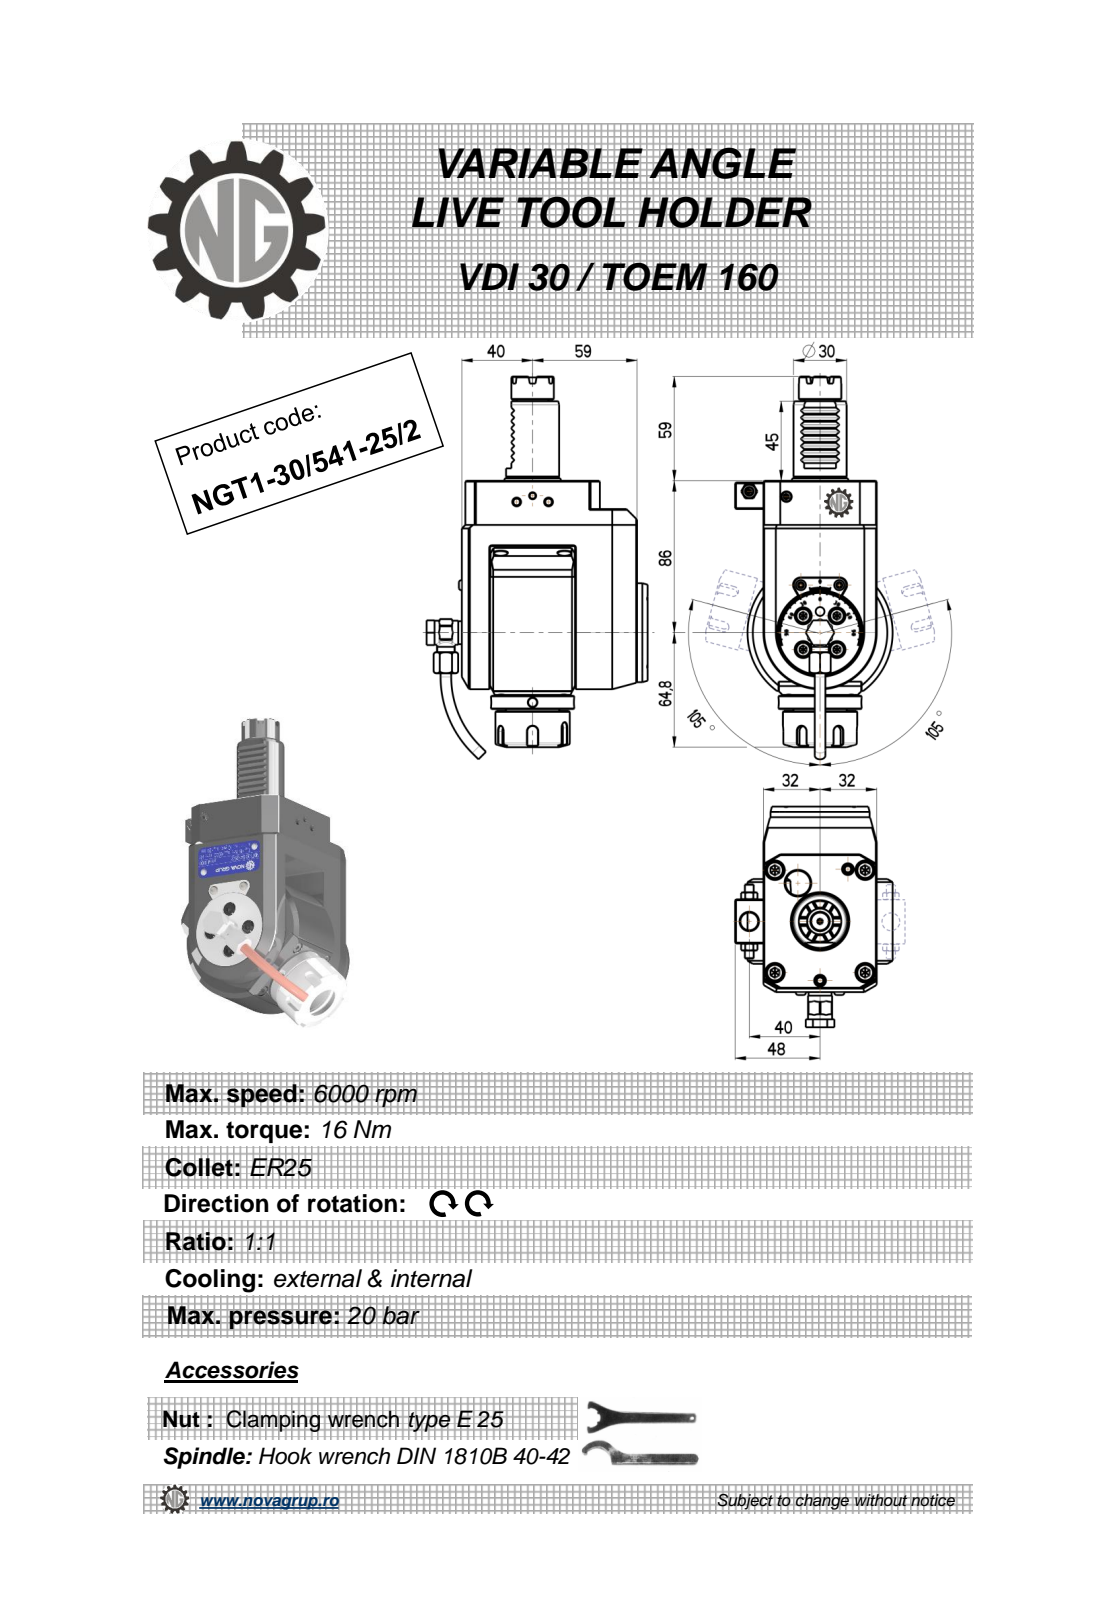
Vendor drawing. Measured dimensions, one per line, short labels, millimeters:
name: NGT1_30_541_25_2
written by: PRO/ENGINEER BY PARAMETRIC TECHNOLOGY CORPORATION, 2010280 (CONFIG_CONTROL_DESIGN)
unit: mm
bodies: 1 solid, 593 faces (262 planar, 144 cylindrical, 187 other)
size: 216.67 × 124.9 × 89
volume: 795 341 mm³; area: 74 501 mm²
holes: 5× ⌀4, 2× ⌀10, 1× ⌀3, 1× ⌀4.2, 1× ⌀6.2, 1× ⌀9, 1× ⌀9.5, 1× ⌀11, 1× ⌀20.3
bosses: 2× ⌀6, 2× ⌀5.7, 1× ⌀56, 1× ⌀42, 1× ⌀40, 1× ⌀32.99, 1× ⌀30, 1× ⌀24
rounds: 12× R0.26, 8× R0.3, 6× R0.16, 5× R3, 4× R0.5, 2× R1, 1× R7.6, 1× R7.7
face distances: 64, 16, 37, 6, 99, 105, 14, 62, 21, 83
hole spacings: 0.4, 38.95, 40, 49, 49.4, 63.25, 63.56, 89.44
